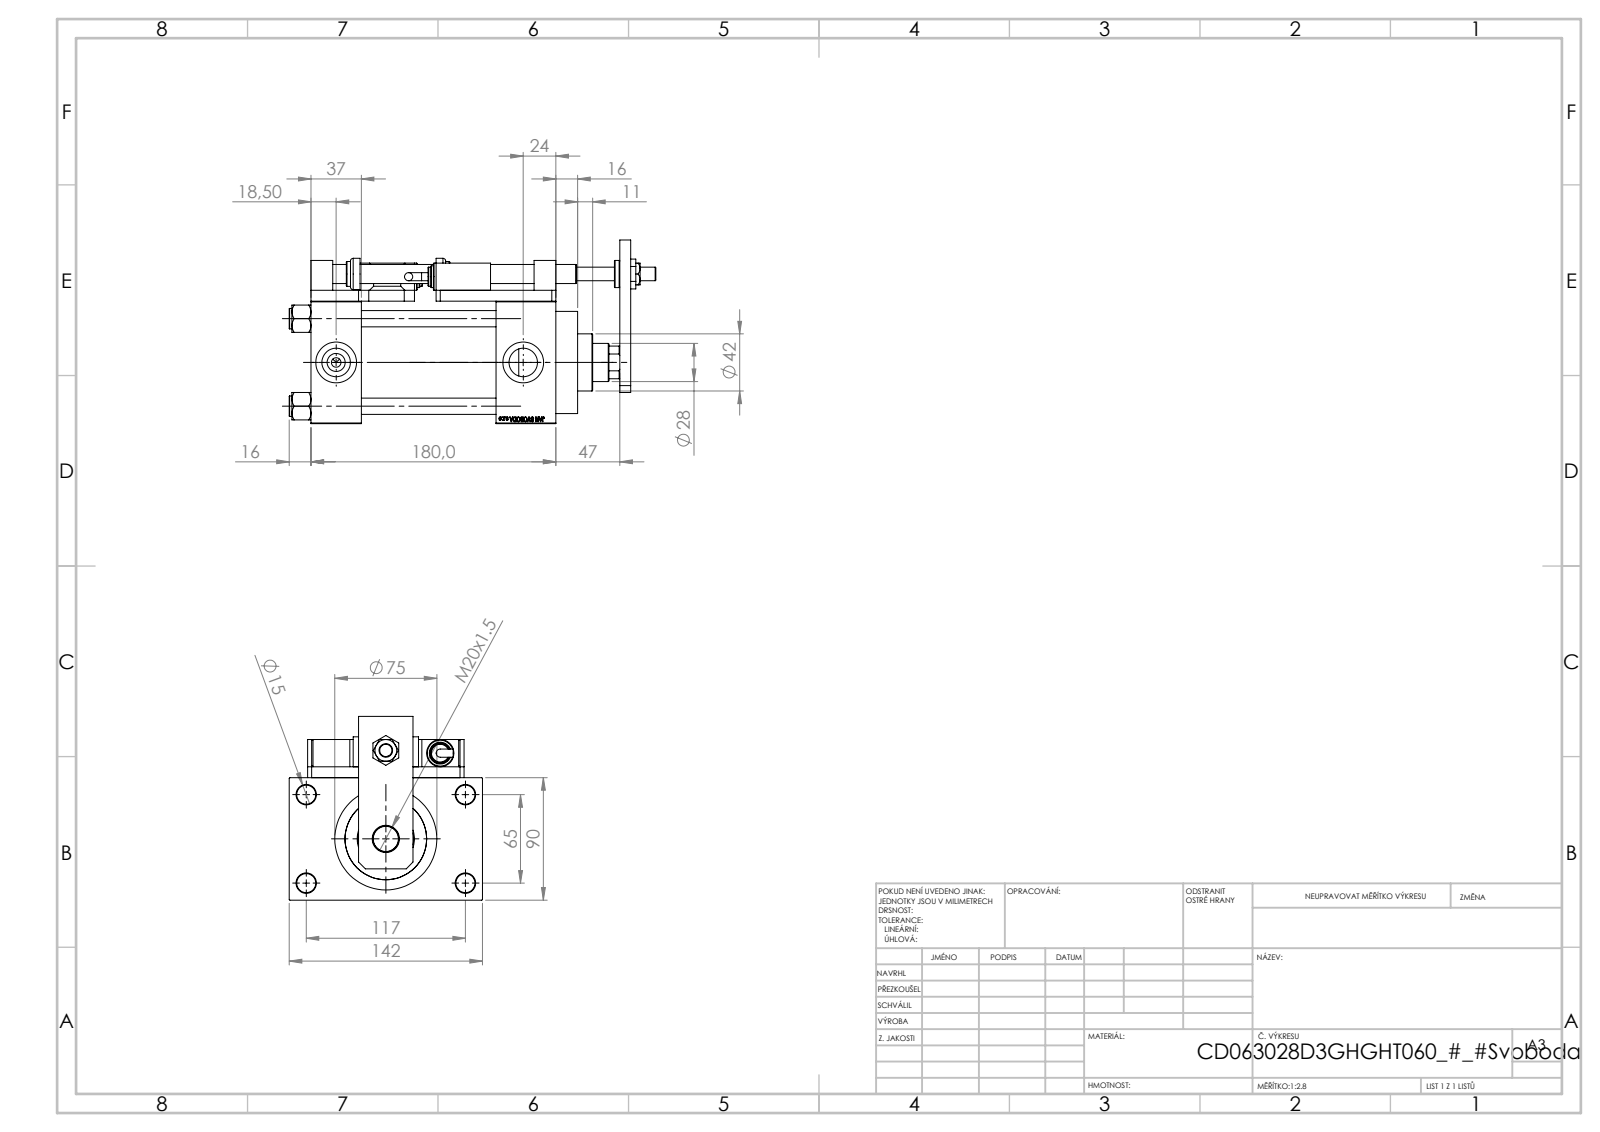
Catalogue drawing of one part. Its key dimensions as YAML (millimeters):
part_name: "V215CD_D_Body; V215CD_NUT_M5_D; V215CD_SWITCH_Q_ZARAZKA; V215CD_VCP_D (+7 more)"
step_written_by: "SolidWorks 2019 (CONFIG_CONTROL_DESIGN)"
units: millimeters
bodies: {solids: 26, faces: 1432, planar: 666, cylindrical: 167, other: 599}
overall_size: [269.5, 142, 135]
volume: 1430000
surface_area: 318080
round_holes:
  - {diameter: 14, count: 5}
  - {diameter: 8.5, count: 4}
  - {diameter: 12, count: 4}
  - {diameter: 13.5, count: 4}
  - {diameter: 20.96, count: 4}
  - {diameter: 30, count: 4}
  - {diameter: 7, count: 3}
  - {diameter: 10, count: 1}
  - {diameter: 18.5, count: 1}
  - {diameter: 20, count: 1}
  - {diameter: 28, count: 1}
  - {diameter: 31, count: 1}
round_bosses_or_shafts:
  - {diameter: 15, count: 4}
  - {diameter: 20, count: 3}
  - {diameter: 16, count: 2}
  - {diameter: 14, count: 2}
  - {diameter: 6, count: 2}
  - {diameter: 75, count: 1}
  - {diameter: 69, count: 1}
  - {diameter: 42, count: 1}
partial_cylinders:
  - {radius: 7.5, count: 4}
  - {radius: 13.5, count: 1}
face_to_face_distances: [8, 99, 90, 44, 180, 37, 143, 98, 136, 16]
hole_center_spacings: [66.92, 26.35, 45.47, 64.3, 69.81, 90.65, 111.34, 65]
